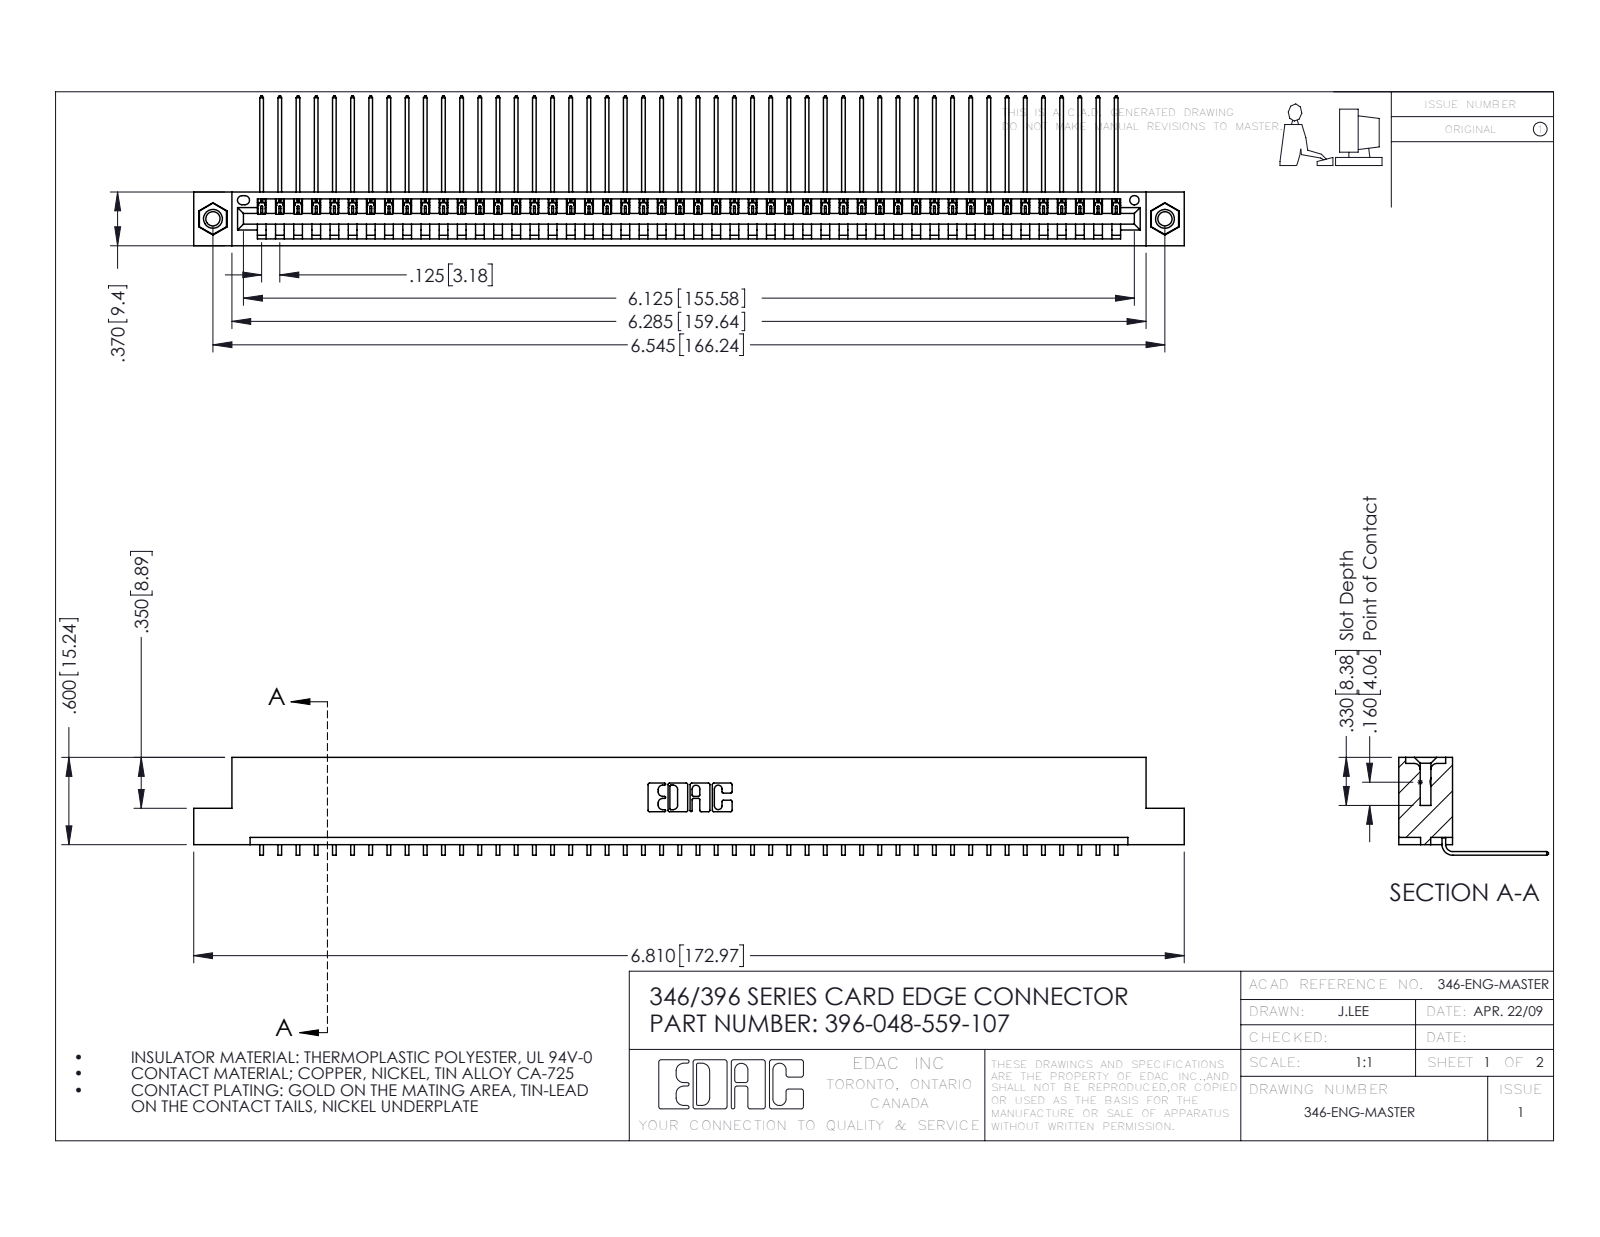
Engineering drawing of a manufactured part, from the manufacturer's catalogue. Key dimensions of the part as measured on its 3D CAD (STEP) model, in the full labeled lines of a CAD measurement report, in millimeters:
Part name (STEP PRODUCT): 345-292-001_558 559 Tail - 1; 396-048-559-107; 346 Part_Flush Mounting Lugs - 0.156 Dia-TI; 345-250-001_345-250-005-103
STEP written by: SolidWorks 2016 (CONFIG_CONTROL_DESIGN)
Units: millimetres
Bodies: 51 solids, 3062 faces (2124 planar, 922 cylindrical, 16 other)
Overall size (bounding box): 173 × 26.2 × 17.1
Volume: 16 750 mm³ · Surface area: 21 980 mm²
Round holes (diameter × count): ⌀2.5 ×2, ⌀3.2 ×2, ⌀4 ×2, ⌀1.6 ×1
Round bosses / shafts (diameter × count): ⌀3.9 ×2
Partial cylindrical surfaces — rounded edges, fillets, slot ends (radius × count): R0.2 ×96, R0.3 ×22, R0.2 ×6, R0.8 ×6, R0.7 ×3, R0.8 ×2, R1 ×2, R0.4 ×1
Main face-to-face distances: 1.2, 8.2, 9.4, 0.6, 6.4, 1.8, 7.6, 3.8, 5.6, 2.5
Hole centre spacings: 6.2, 160.9, 166.2
